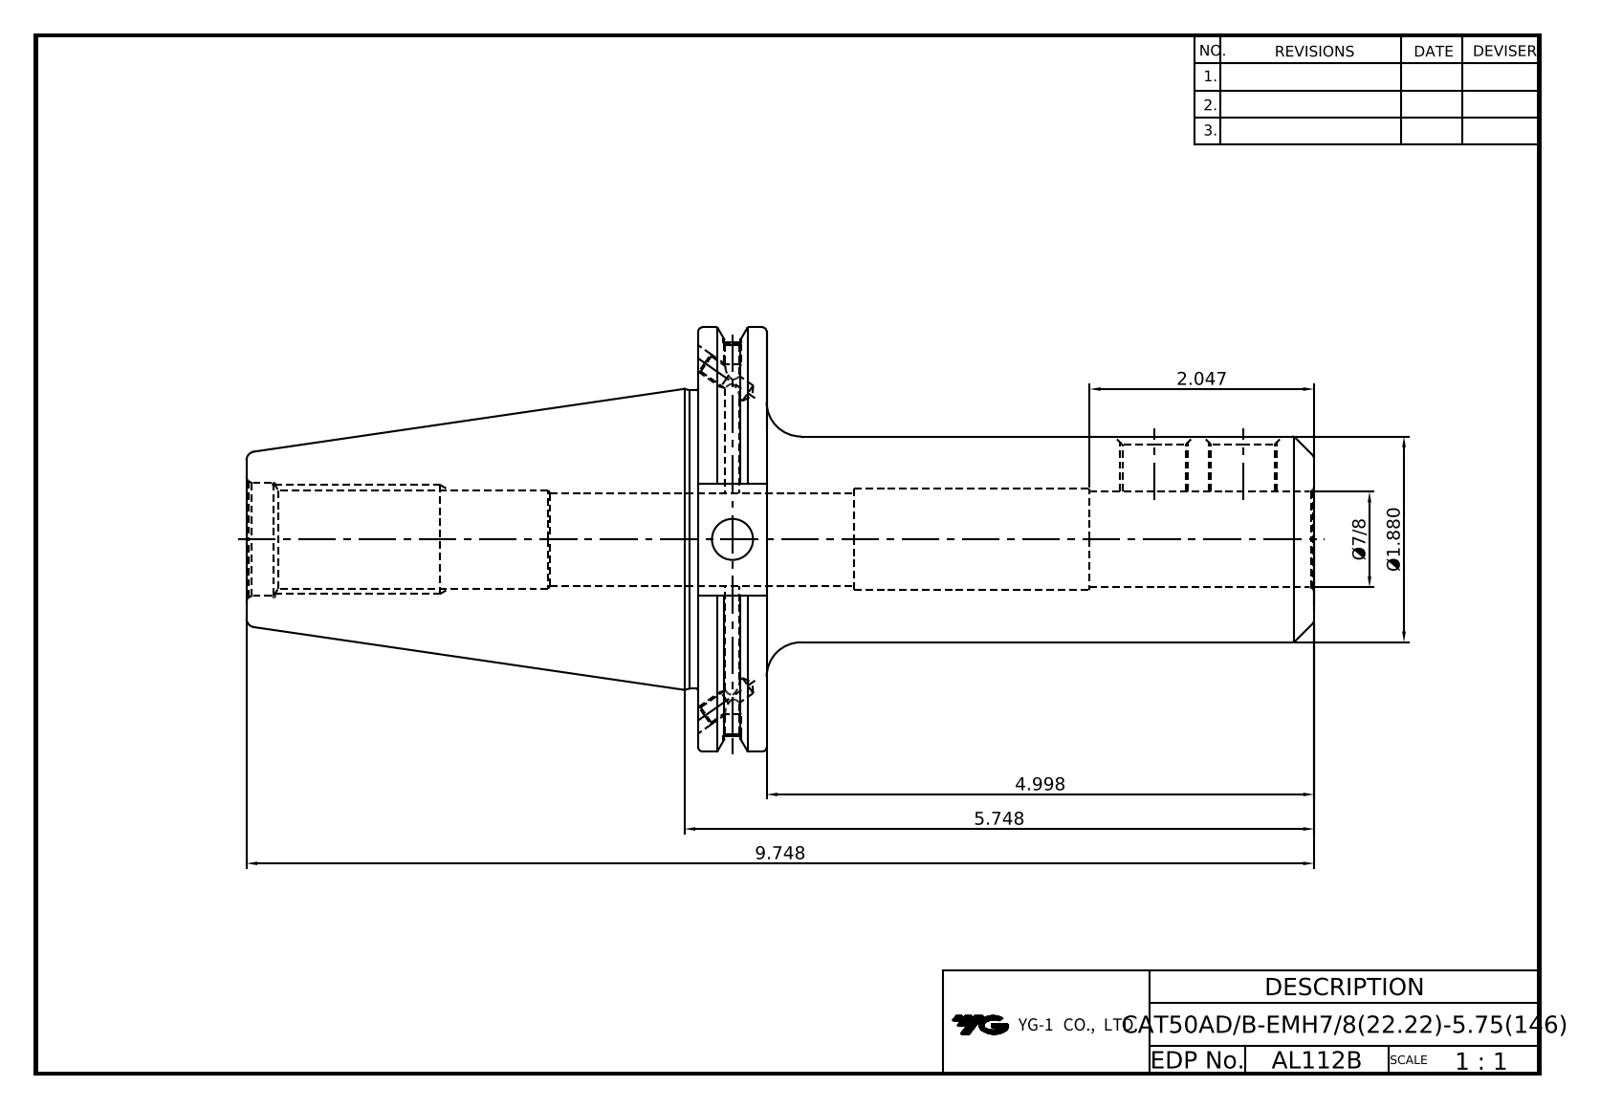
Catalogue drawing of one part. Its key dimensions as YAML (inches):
part_name: "LO-CAT50ADB-EMH22.225-146"
step_written_by: "Autodesk Inventor 2025 (AUTOMOTIVE_DESIGN)"
units: inches
bodies: {solids: 1, faces: 87, planar: 37, cylindrical: 27, other: 23}
overall_size: [9.748, 3.875, 3.728]
volume: 29.91
surface_area: 112.2
round_holes:
  - {diameter: 0.128, count: 2}
  - {diameter: 0.163, count: 2}
  - {diameter: 0.165, count: 2}
  - {diameter: 0.197, count: 2}
  - {diameter: 0.565, count: 2}
  - {diameter: 0.375, count: 1}
  - {diameter: 0.865, count: 1}
  - {diameter: 0.875, count: 1}
  - {diameter: 0.922, count: 1}
  - {diameter: 1.031, count: 1}
round_bosses_or_shafts:
  - {diameter: 3.875, count: 1}
  - {diameter: 3.594, count: 1}
  - {diameter: 2.726, count: 1}
  - {diameter: 1.88, count: 1}
face_to_face_distances: [0.625, 5.623, 4.998, 4.125, 4.75, 9.748, 2.875, 1.02, 4.363, 0.238]
hole_center_spacings: [0.811]
